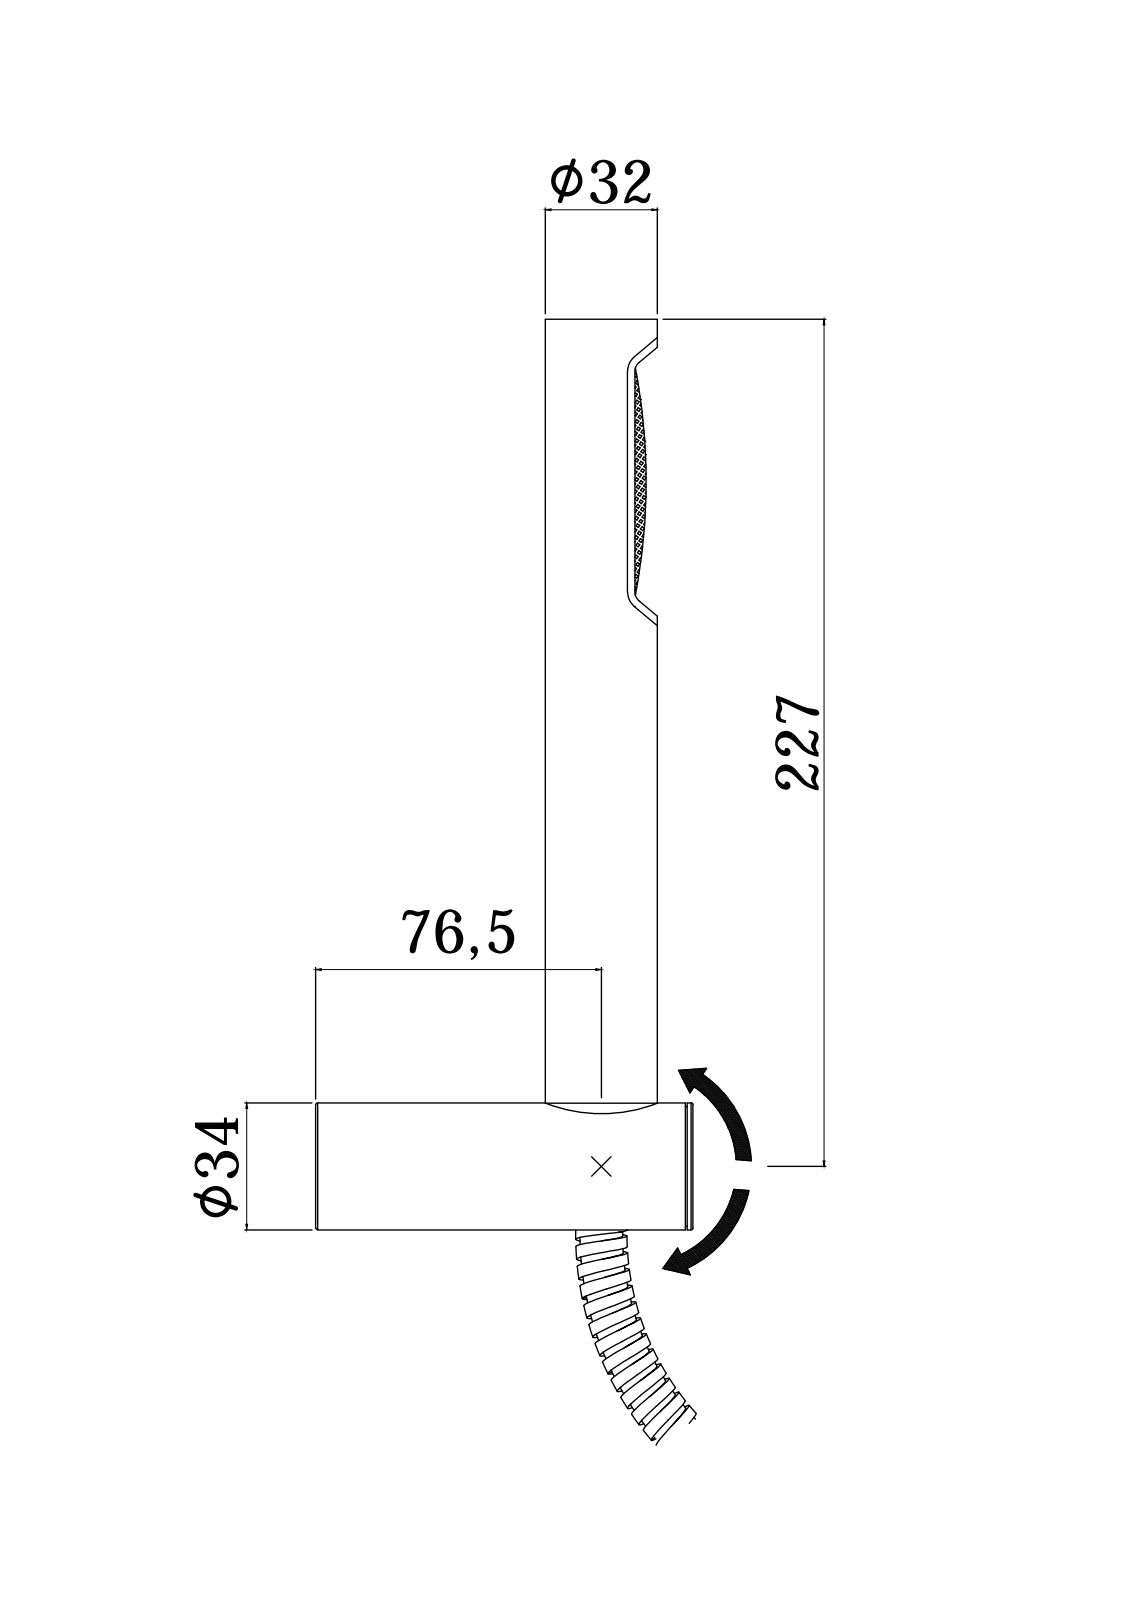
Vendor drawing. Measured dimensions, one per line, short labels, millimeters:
name: ZDUP054CR
written by: CREO PARAMETRIC BY PTC INC, 2020044 (CONFIG_CONTROL_DESIGN)
unit: mm
bodies: 3 solids, 380 faces (113 planar, 187 cylindrical, 80 other)
size: 326.3 × 101 × 76
volume: 122 240 mm³; area: 94 436 mm²
holes: 45× ⌀1.5, 1× ⌀3.5, 1× ⌀15.8, 1× ⌀16, 1× ⌀20.5, 1× ⌀21.5, 1× ⌀27.8, 1× ⌀28, 1× ⌀29, 1× ⌀29.5, 1× ⌀30.5, 1× ⌀31.3
bosses: 1× ⌀34.5, 1× ⌀34, 1× ⌀33.8, 1× ⌀33.5, 1× ⌀32, 1× ⌀31, 1× ⌀30, 1× ⌀27.6
rounds: 6× R0.3, 4× R2, 4× R5, 4× R5.2, 2× R7.8, 2× R9.8, 2× R10, 1× R3.65
face distances: 2, 17.5, 19.5, 81.5, 101, 2.5, 10, 99, 79, 96.5
hole spacings: 7.91, 13.76, 20.01, 6.5, 26.39, 13, 4.5, 11.1
